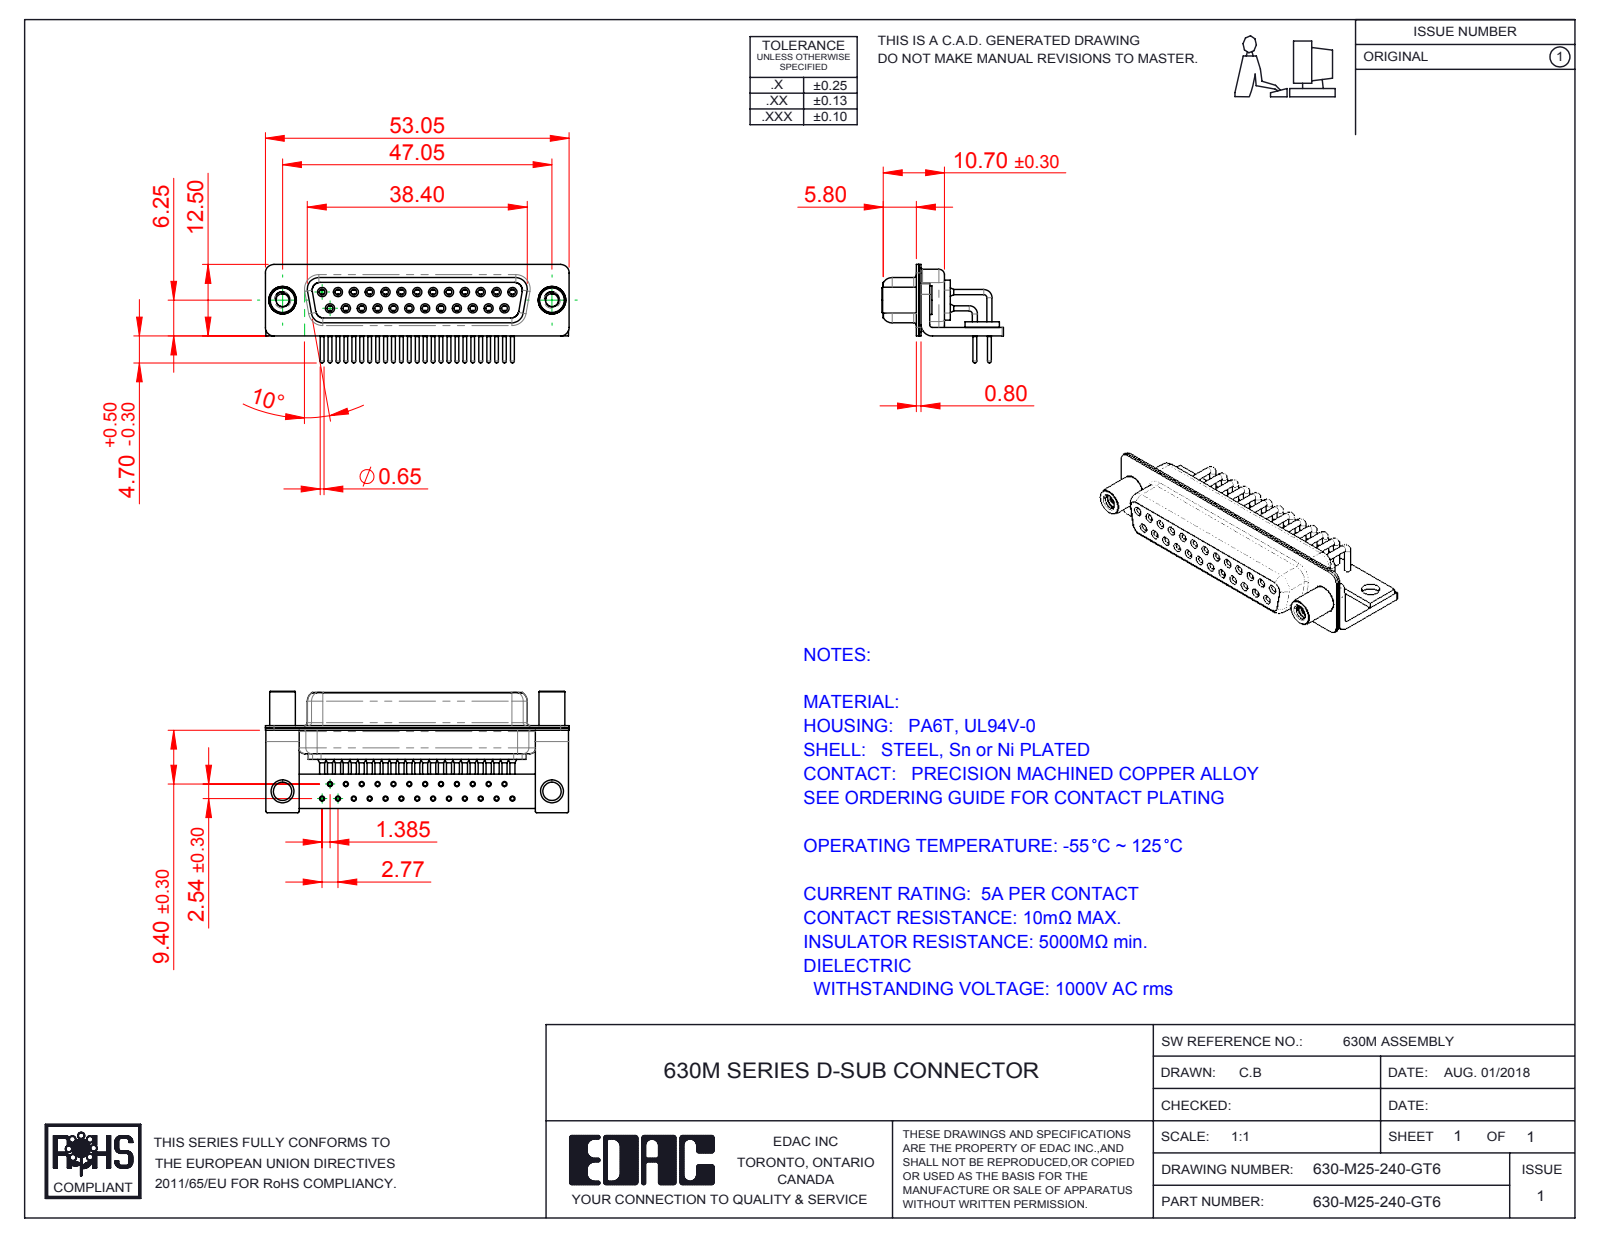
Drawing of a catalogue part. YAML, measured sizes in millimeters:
part_name: "630M Stabilizer Board_25 Contacts; 630M Shell Rear_25 Contacts; 630M Contact Row 1; 630M 4-40 Threaded Standoff (+5 more)"
step_written_by: "SolidWorks 2016 (CONFIG_CONTROL_DESIGN)"
units: millimeters
bodies: {solids: 33, faces: 1754, planar: 470, cylindrical: 826, other: 458}
overall_size: [53.05, 21.2, 17.2]
volume: 4578
surface_area: 11419
round_holes:
  - {diameter: 0.9, count: 25}
  - {diameter: 1, count: 25}
  - {diameter: 1.1, count: 25}
  - {diameter: 1.7, count: 25}
  - {diameter: 1.8, count: 25}
  - {diameter: 2, count: 25}
  - {diameter: 2.26, count: 2}
  - {diameter: 3.2, count: 2}
  - {diameter: 4, count: 2}
  - {diameter: 4.8, count: 2}
round_bosses_or_shafts:
  - {diameter: 1.6, count: 25}
  - {diameter: 1.5, count: 25}
  - {diameter: 0.9, count: 25}
  - {diameter: 0.65, count: 25}
  - {diameter: 5, count: 2}
  - {diameter: 4.9, count: 2}
  - {diameter: 4.5, count: 2}
partial_cylinders:
  - {radius: 0.25, count: 16}
  - {radius: 1.5, count: 16}
  - {radius: 2, count: 13}
  - {radius: 1.35, count: 10}
  - {radius: 1.6, count: 8}
  - {radius: 0.5, count: 5}
  - {radius: 0.6, count: 4}
  - {radius: 0.65, count: 4}
face_to_face_distances: [0.4, 2.3, 1.9, 1.45, 8.95, 0.85, 9.35, 0.8, 6.2, 1]
hole_center_spacings: [2.77, 5.54, 8.31, 11.08, 13.85, 3.16, 4.87, 16.62]
